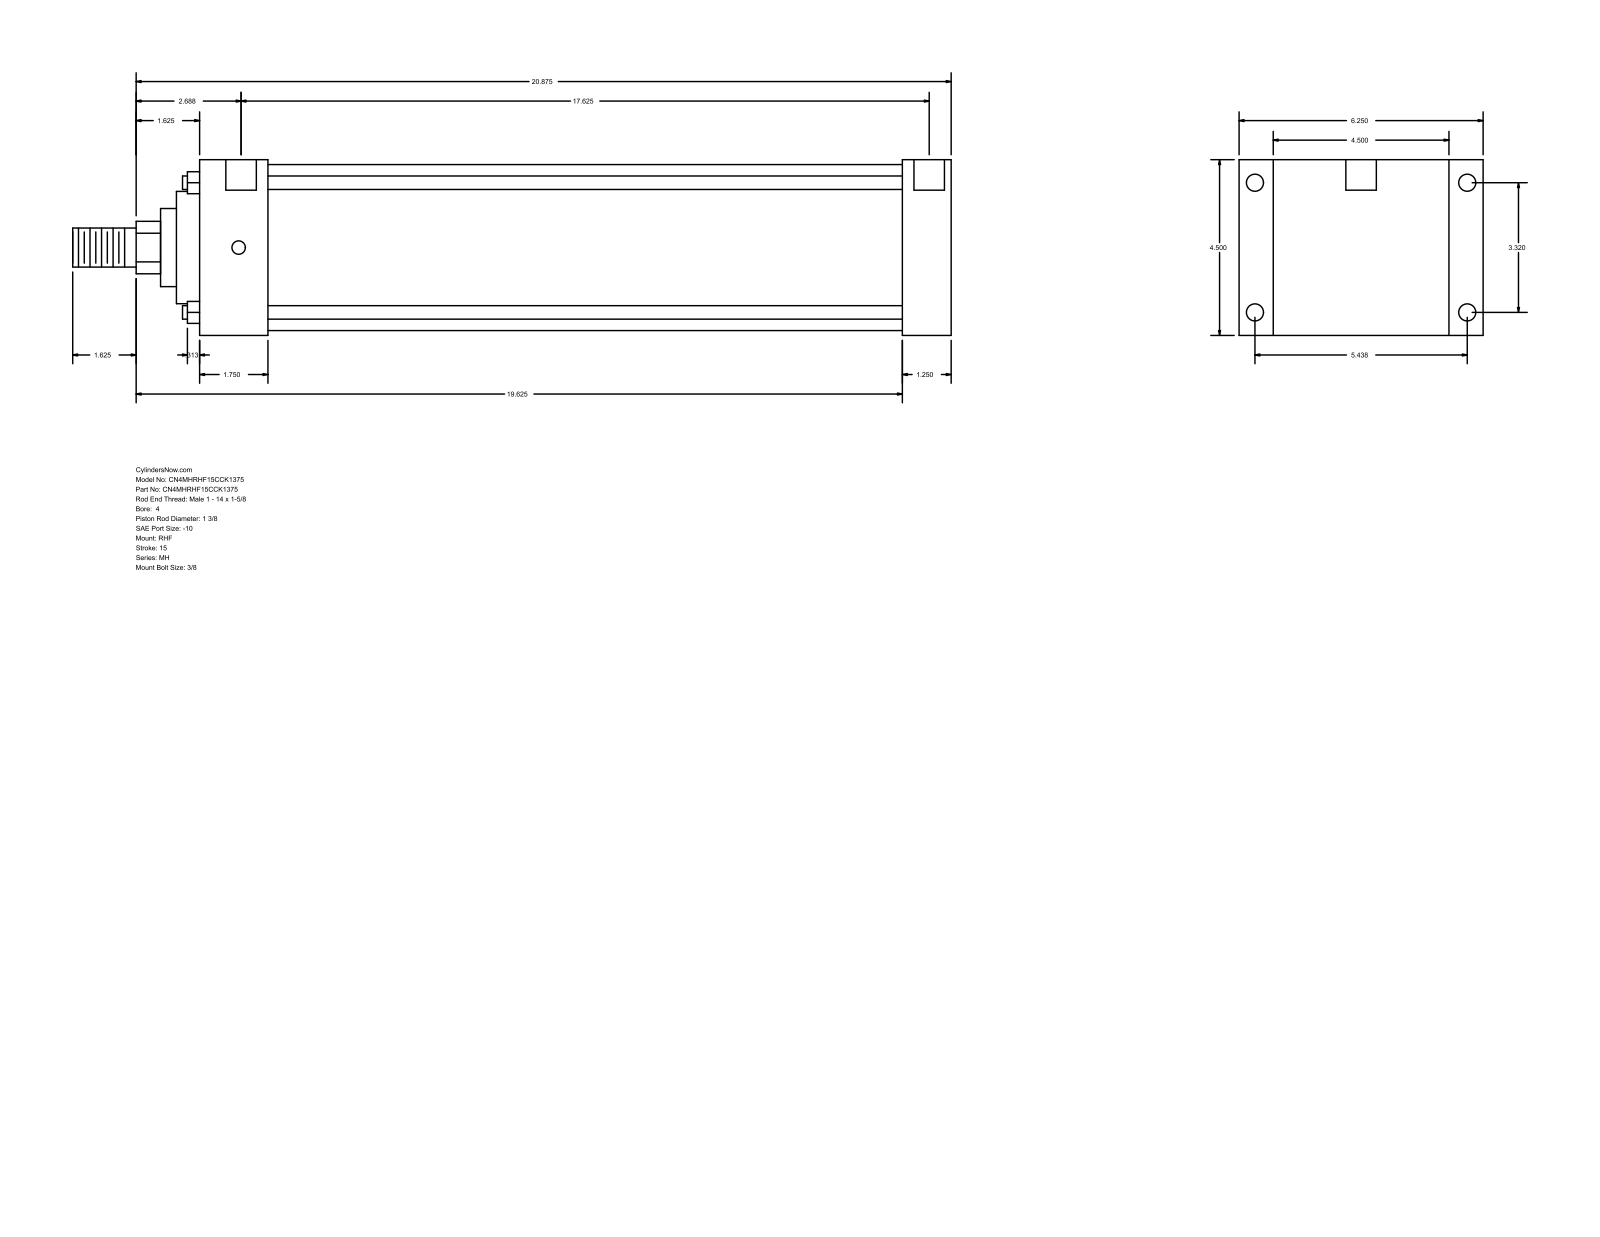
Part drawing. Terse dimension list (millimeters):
name: MH_RHF__0400_1.375
written by: GSSL Pune (CONFIG_CONTROL_DESIGN)
unit: mm
bodies: 0 solids, 90 faces (61 planar, 29 cylindrical, 0 other)
size: 571.5 × 158.75 × 114.3
holes: 4× ⌀8.73, 4× ⌀11.13, 2× ⌀19.84
bosses: 4× ⌀8.76, 1× ⌀107.95, 1× ⌀73.03, 1× ⌀50.8, 1× ⌀34.92, 1× ⌀25.4
rounds: 1× R17.06
face distances: 114.3, 31.75, 457.21, 488.96, 22.23, 136.53, 44.45, 412.76, 444.51, 158.76
hole spacings: 84.32, 138.12, 161.82, 450.85, 1.58, 1.59, 447.68, 449.26
